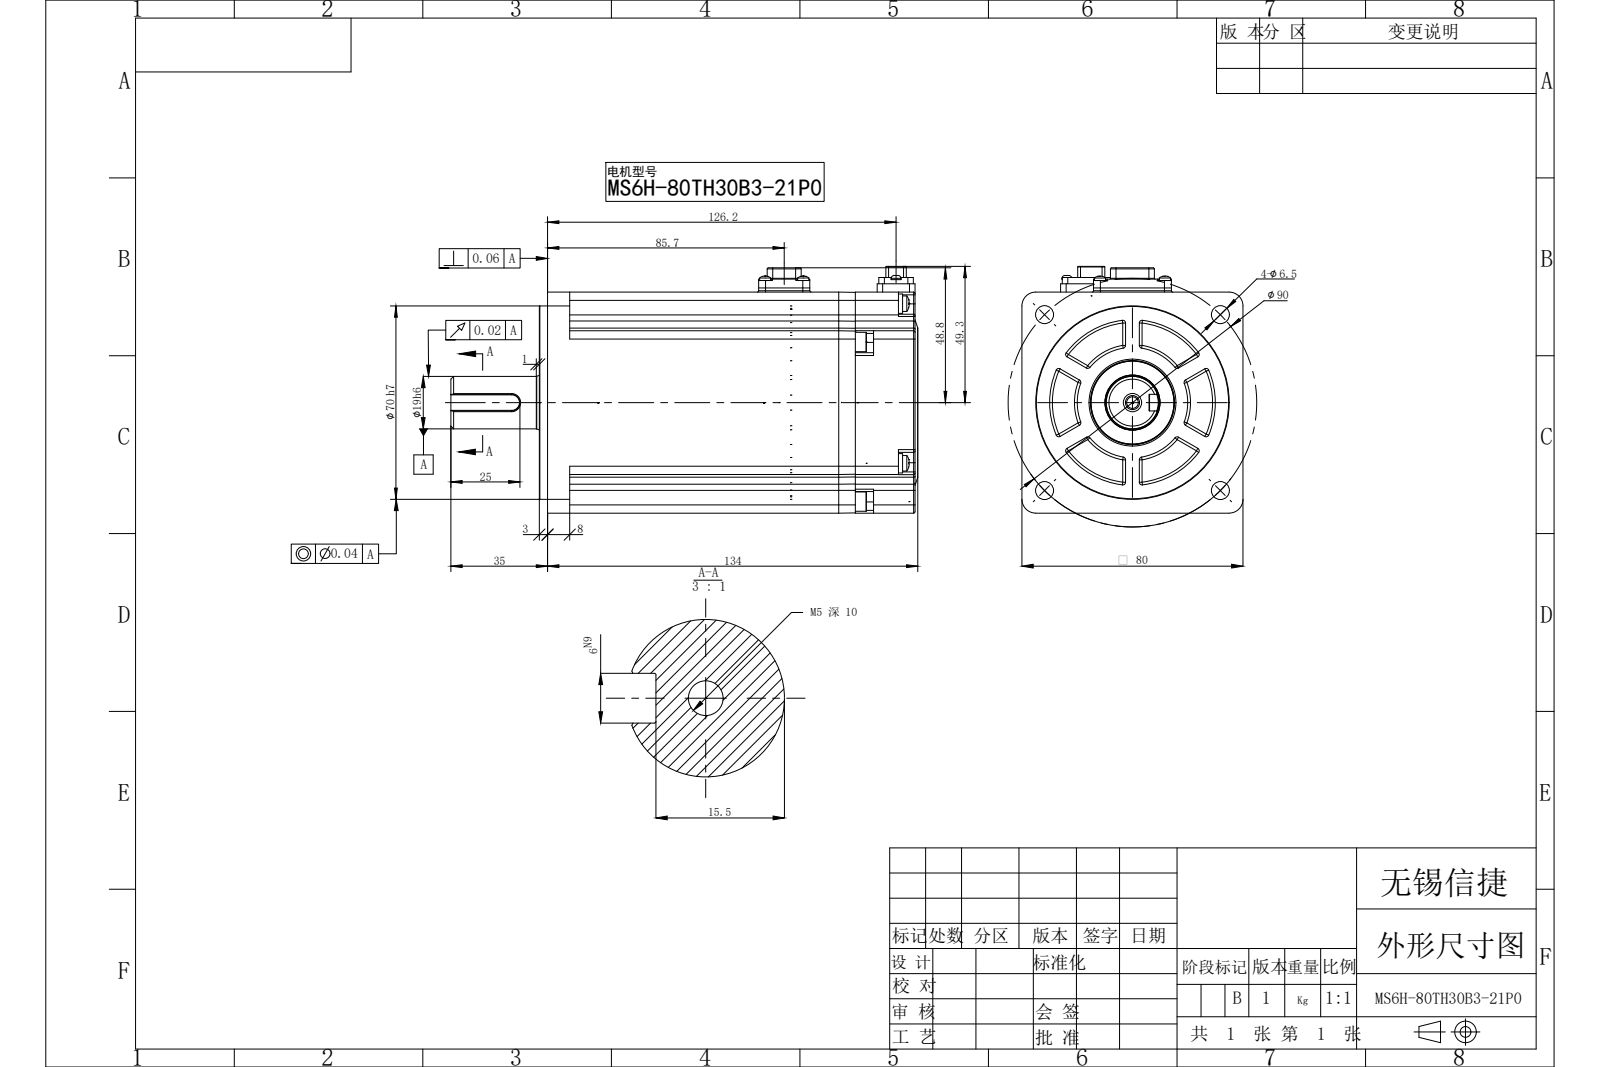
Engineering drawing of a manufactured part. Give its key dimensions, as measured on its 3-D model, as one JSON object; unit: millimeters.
{"part_name": "MS6H-80TH30B3-21P0", "step_written_by": "SolidWorks 2022 (CONFIG_CONTROL_DESIGN)", "units": "millimeters", "bodies": {"solids": 0, "faces": 818, "planar": 369, "cylindrical": 278, "other": 171}, "overall_size": [169, 89.3, 80], "round_holes": [[2.1, 4], [6.5, 4], [1.6, 2], [4.2, 1], [20, 1]], "round_bosses_or_shafts": [[7, 8], [5.6, 4], [4, 4], [3.5, 2], [70, 1], [30, 1], [19.8, 1], [19, 1]], "partial_cylinders_radius": [[1, 50], [0.5, 33], [3, 17], [0.2, 13], [2, 12], [0.3, 10], [3.75, 8], [0.6, 4]], "face_to_face_distances": [80, 14, 66, 133, 52, 1, 134, 3, 137, 136], "hole_center_spacings": [45, 63.64, 8, 16.6, 18.43, 90, 23.5, 36.86]}
